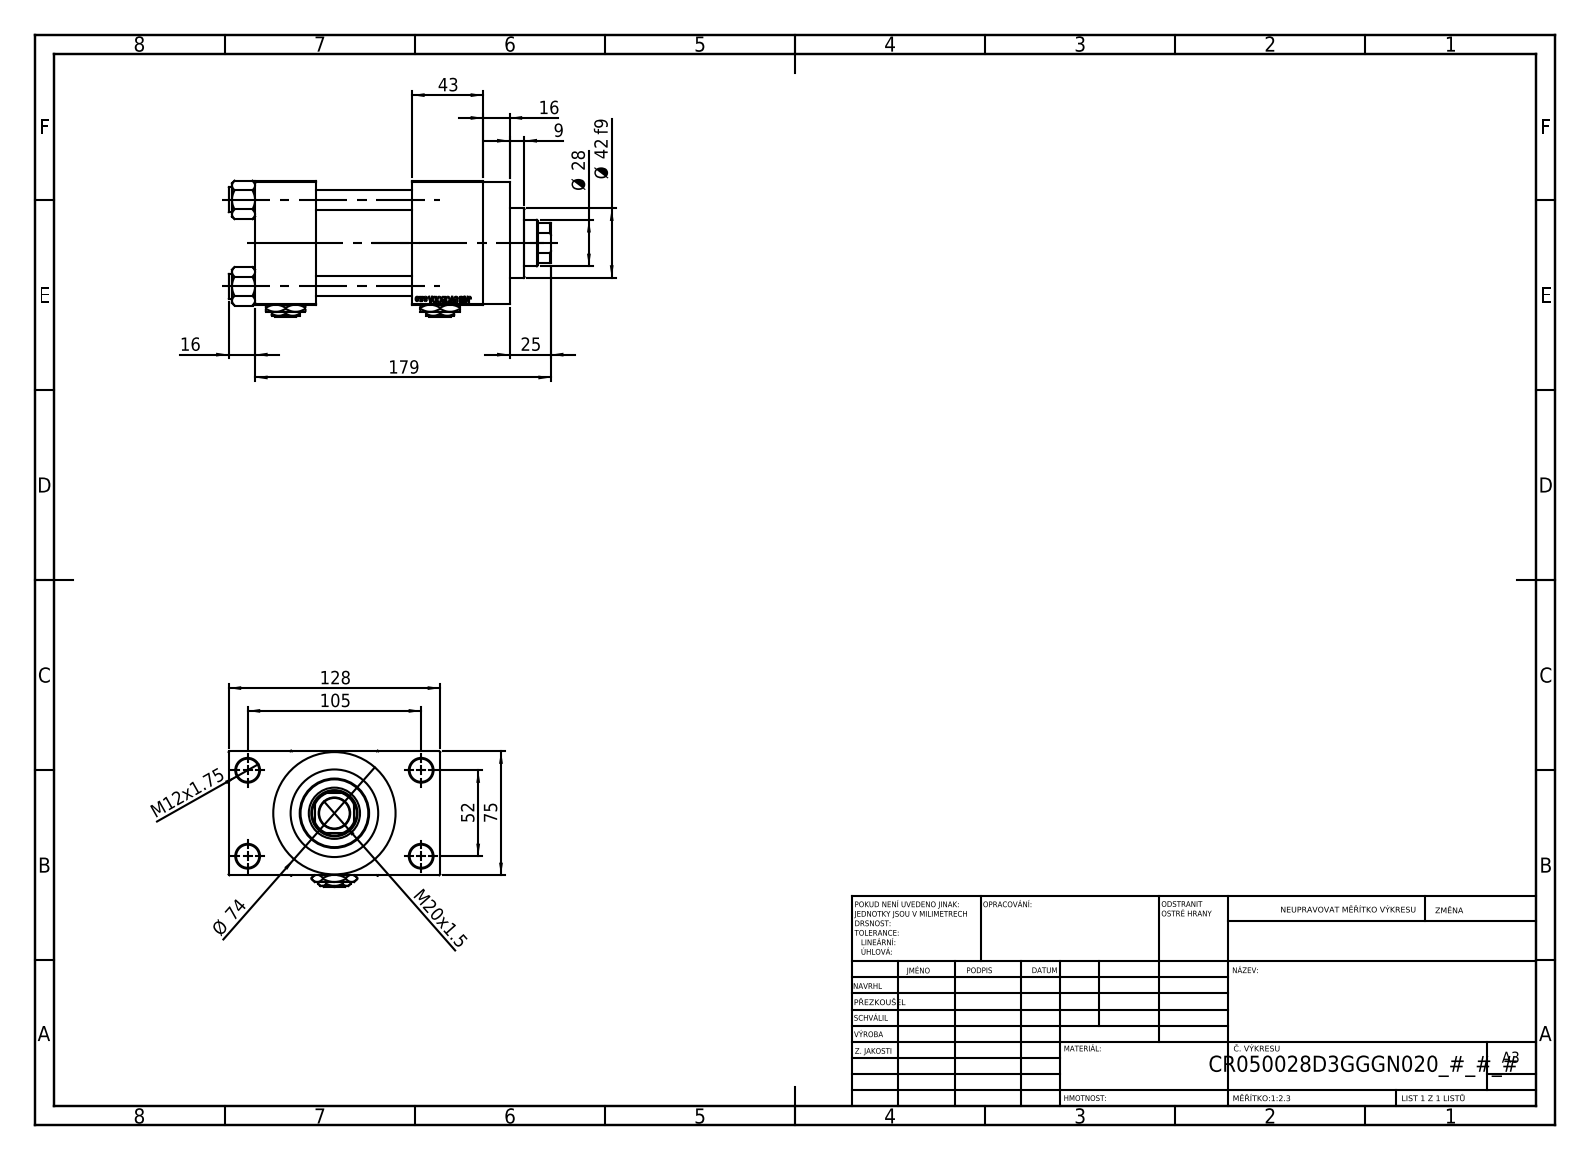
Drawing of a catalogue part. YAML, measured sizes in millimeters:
part_name: "V215CR_D_TYCINKA; NUT_M5_D; V215_VC_A; V215CR_D_Body (+2 more)"
step_written_by: "SolidWorks 2019 (CONFIG_CONTROL_DESIGN)"
units: millimeters
bodies: {solids: 13, faces: 1205, planar: 545, cylindrical: 100, other: 560}
overall_size: [195, 128, 82.27]
volume: 810868
surface_area: 173104
round_holes:
  - {diameter: 12, count: 4}
  - {diameter: 14, count: 4}
  - {diameter: 7, count: 2}
  - {diameter: 20.96, count: 2}
  - {diameter: 30, count: 2}
  - {diameter: 18.5, count: 1}
  - {diameter: 28, count: 1}
  - {diameter: 31, count: 1}
  - {diameter: 41, count: 1}
  - {diameter: 50, count: 1}
  - {diameter: 53, count: 1}
round_bosses_or_shafts:
  - {diameter: 15, count: 4}
  - {diameter: 74, count: 1}
  - {diameter: 56, count: 1}
  - {diameter: 42, count: 1}
partial_cylinders:
  - {radius: 13.5, count: 1}
face_to_face_distances: [75, 58, 37, 95, 101.5, 26.5, 138, 101, 43, 16]
hole_center_spacings: [26.35, 36.98, 52.3, 58.43, 58.59, 78.65, 94.37, 52]
